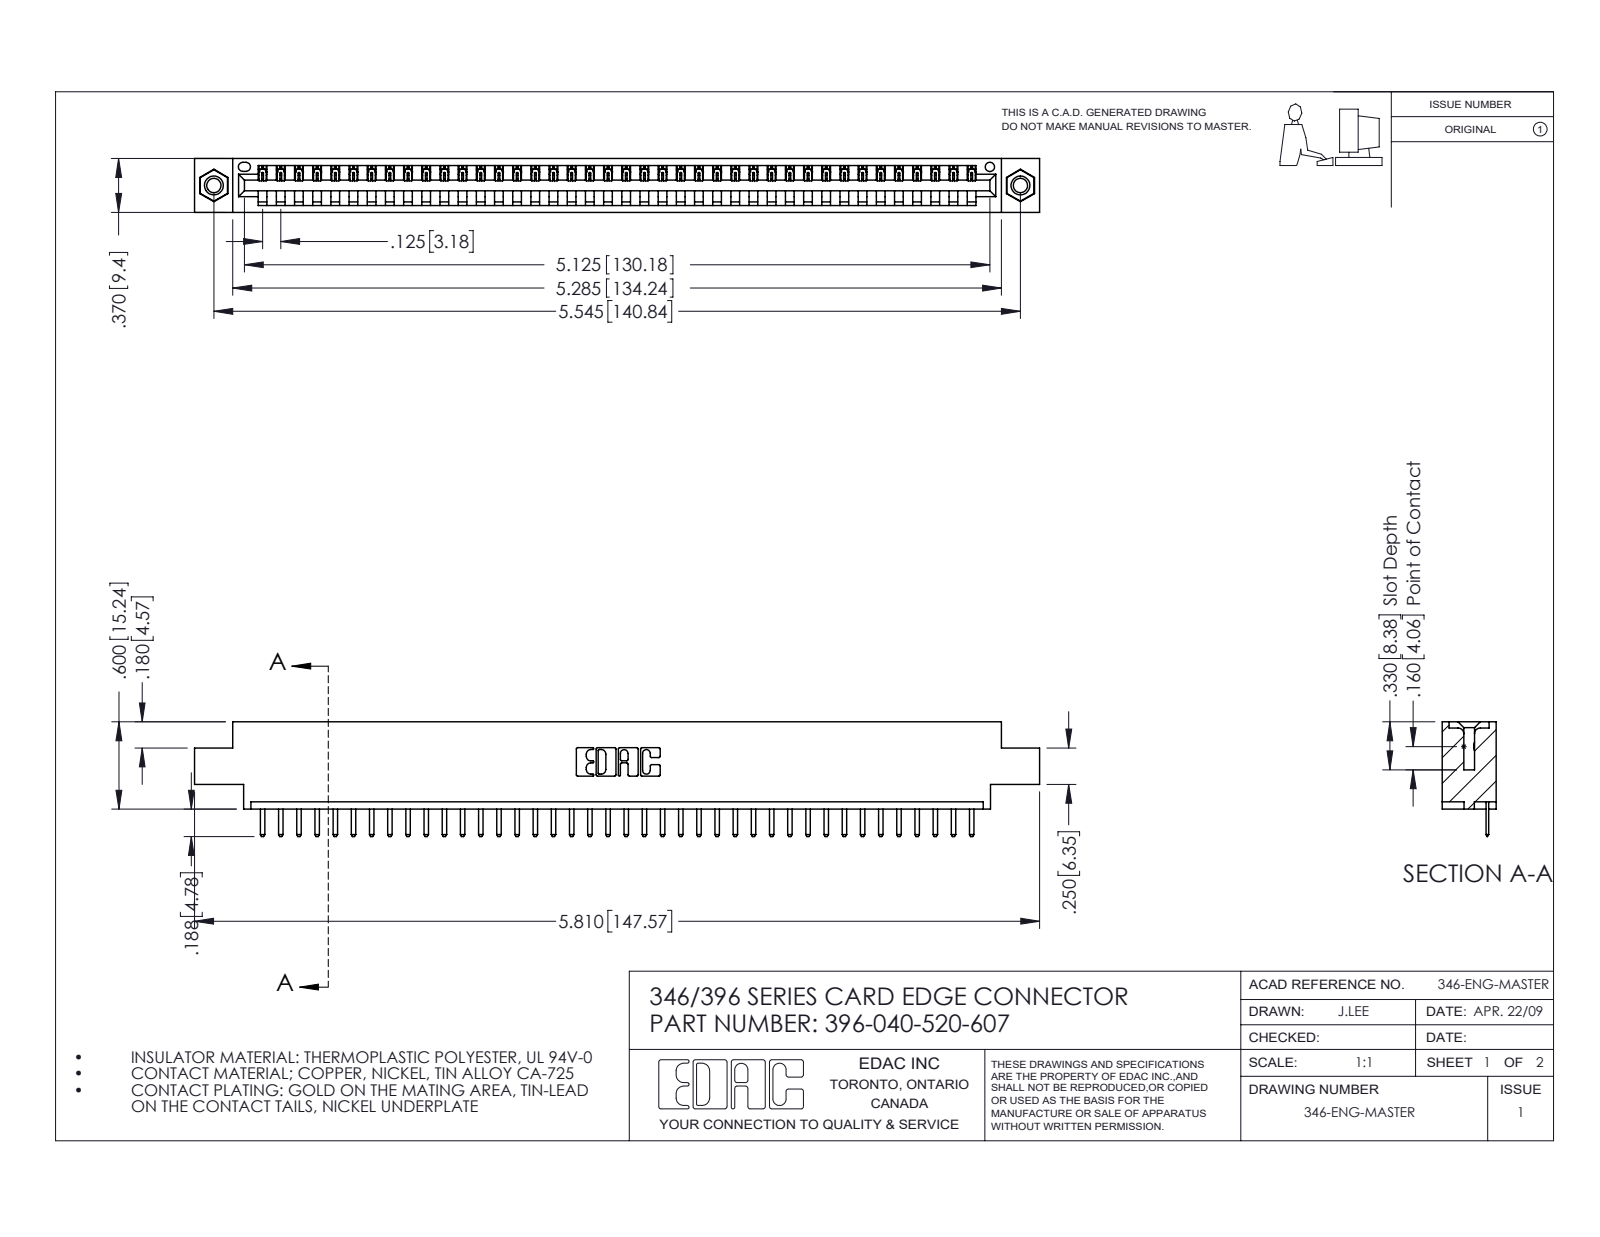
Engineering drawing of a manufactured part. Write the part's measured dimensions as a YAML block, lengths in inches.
part_name: "345-250-001_345-250-005-103; 345-292-001_345-293-120; 396-040-520-607; 346 Part_0.170 Offset - 0.156 Dia-TI"
step_written_by: "SolidWorks 2016 (CONFIG_CONTROL_DESIGN)"
units: inches
bodies: {solids: 43, faces: 2666, planar: 1792, cylindrical: 858, other: 16}
overall_size: [5.81, 0.788, 0.37]
volume: 0.844
surface_area: 26.46
round_holes:
  - {diameter: 0.098, count: 2}
  - {diameter: 0.125, count: 2}
  - {diameter: 0.156, count: 2}
  - {diameter: 0.064, count: 1}
round_bosses_or_shafts:
  - {diameter: 0.155, count: 2}
partial_cylinders:
  - {radius: 0.01, count: 82}
  - {radius: 0.006, count: 80}
  - {radius: 0.01, count: 22}
  - {radius: 0.007, count: 6}
  - {radius: 0.031, count: 6}
  - {radius: 0.026, count: 3}
  - {radius: 0.031, count: 2}
  - {radius: 0.04, count: 2}
face_to_face_distances: [0.048, 0.322, 0.37, 0.25, 0.222, 0.148, 0.1, 0.174, 0.072, 0.298]
hole_center_spacings: [0.246, 5.336, 5.545]
